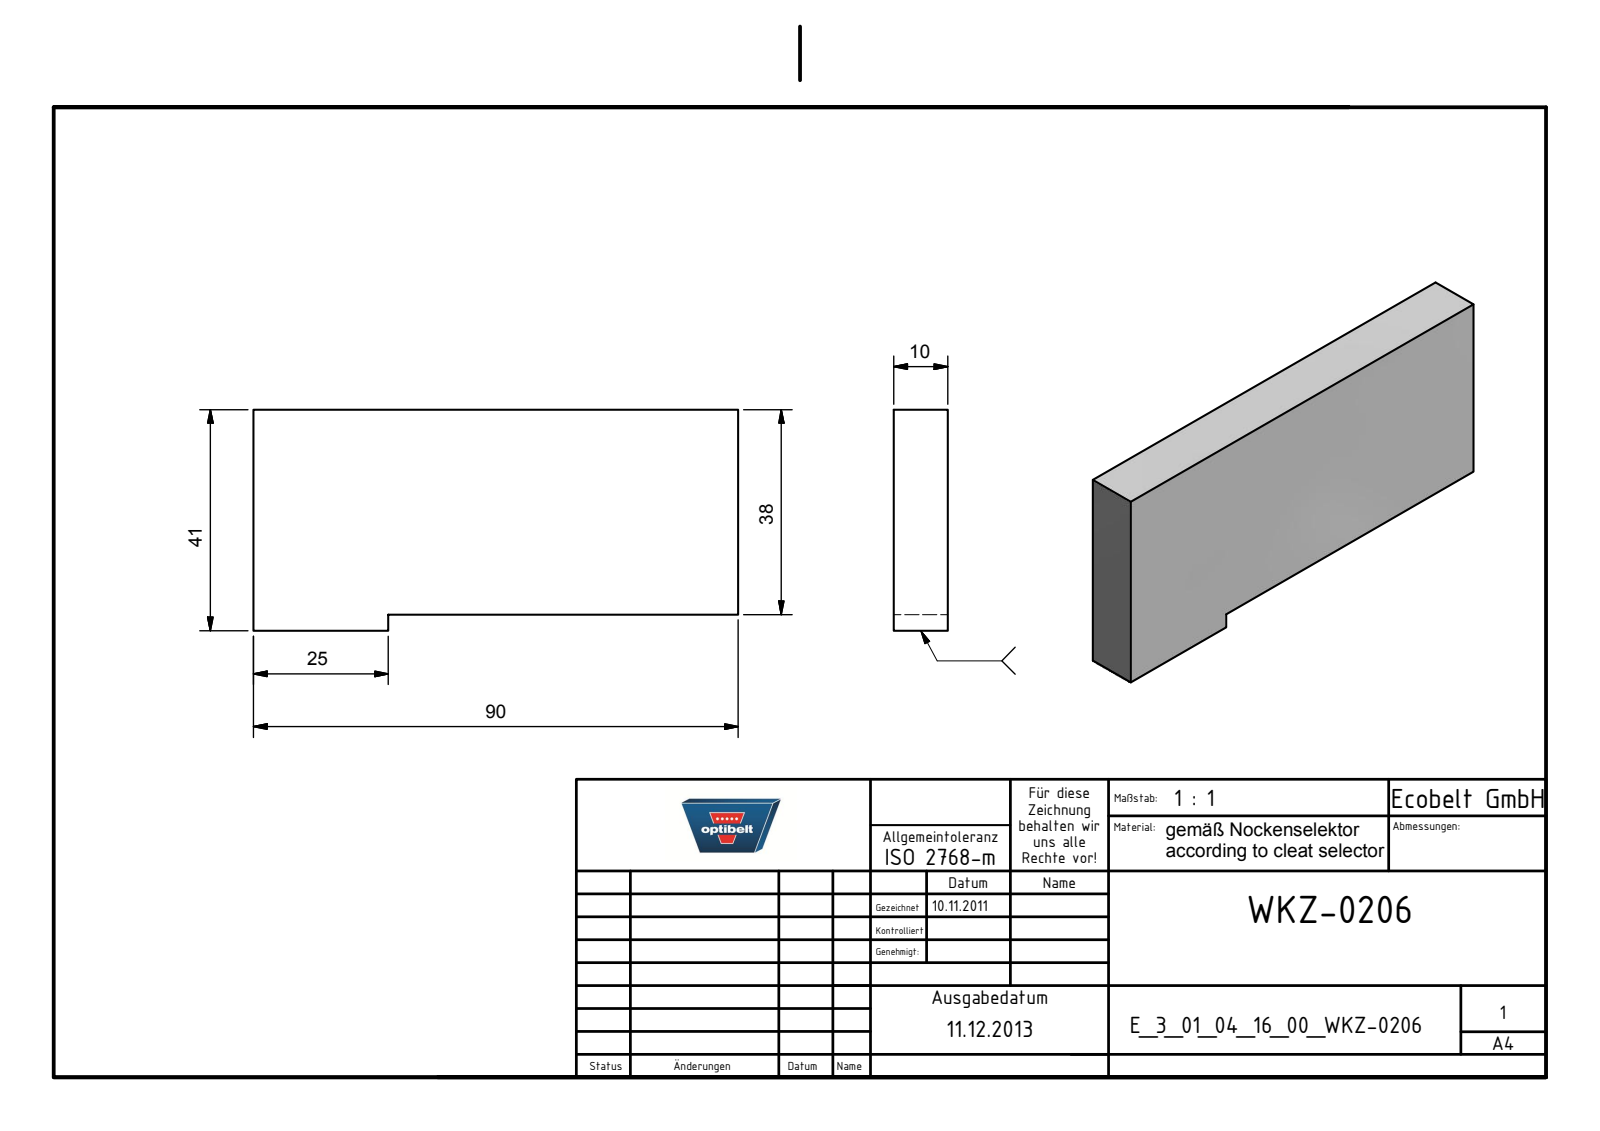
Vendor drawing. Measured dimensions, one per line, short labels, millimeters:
name: E_3_01_04_16_00_WKZ-0206
written by: Autodesk Inventor 2025 (AUTOMOTIVE_DESIGN)
unit: mm
bodies: 1 solid, 8 faces (8 planar, 0 cylindrical, 0 other)
size: 90 × 41 × 10
volume: 34 950 mm³; area: 9 610 mm²
face distances: 10, 38, 90, 3, 41, 25, 65
